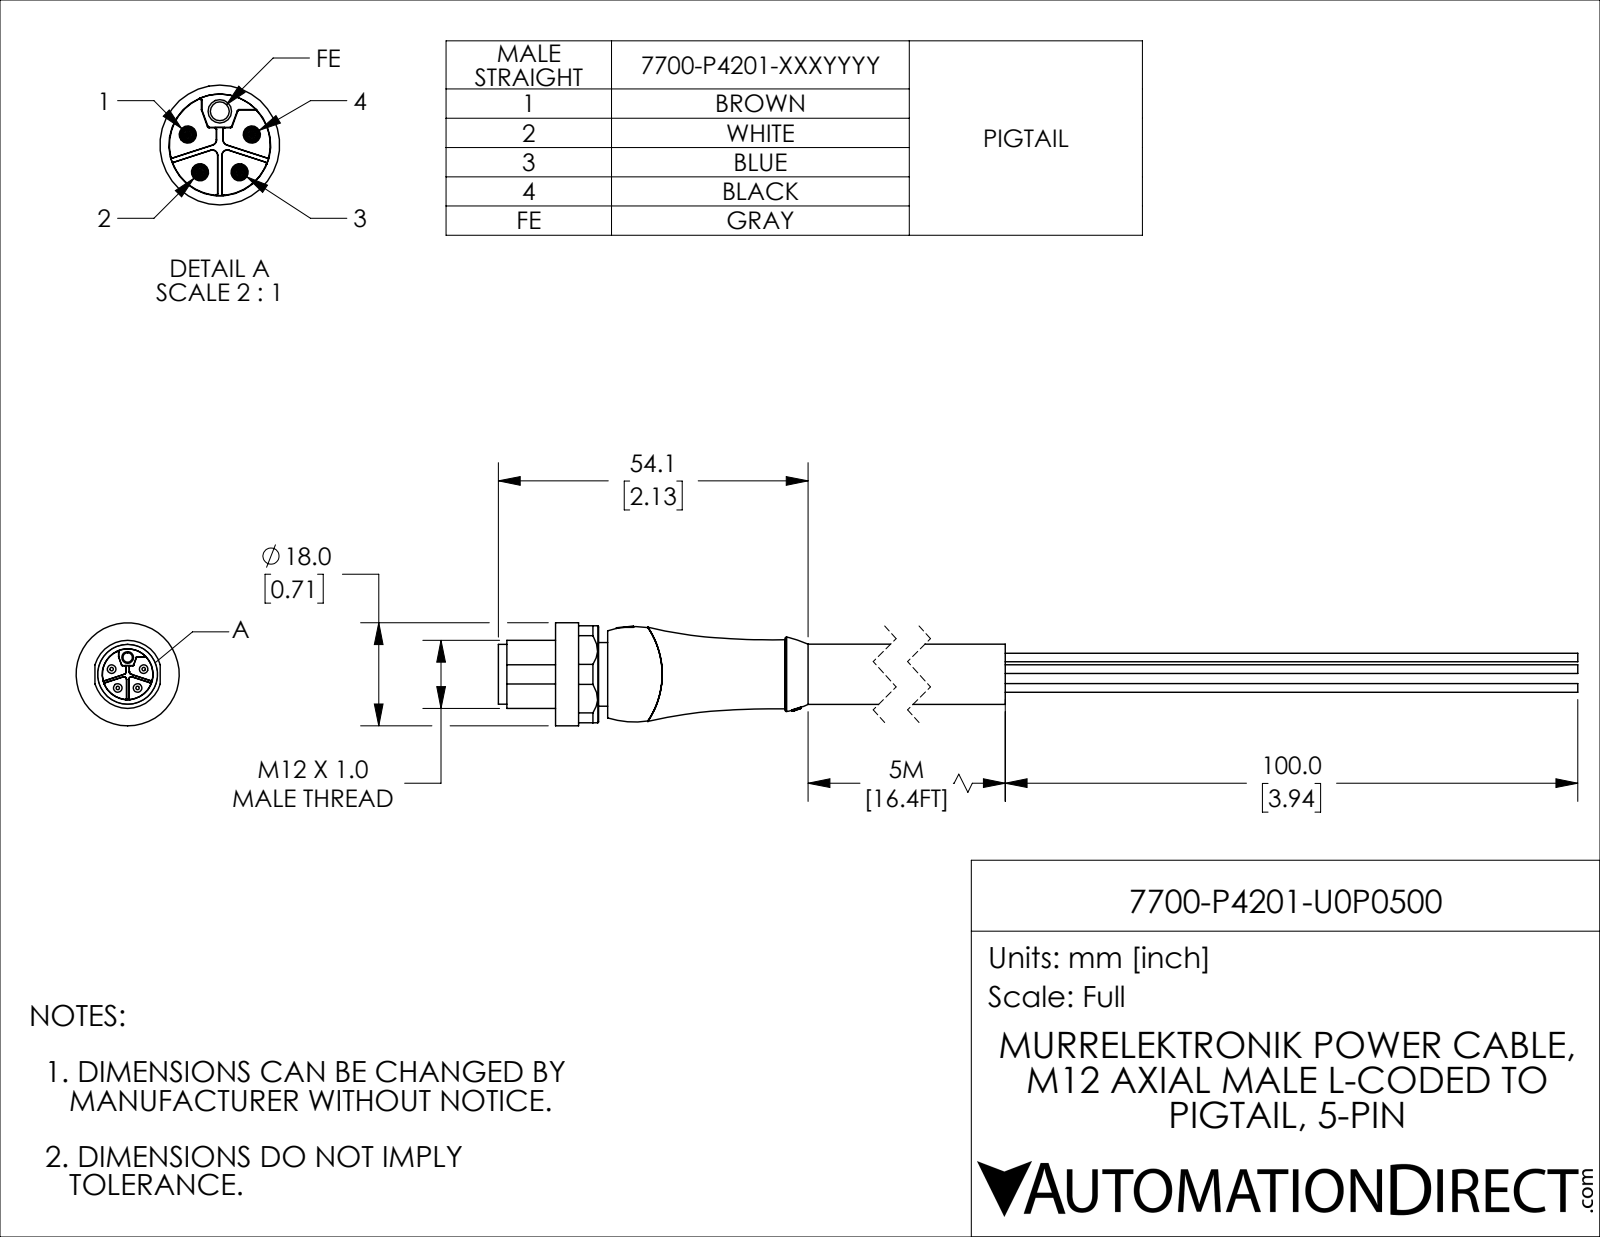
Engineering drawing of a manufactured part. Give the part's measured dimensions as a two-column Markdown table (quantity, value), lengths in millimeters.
| quantity | value |
| --- | --- |
| part name | 7700-P4201-U0P0500 |
| STEP written by | SolidWorks 2021 (CONFIG_CONTROL_DESIGN) |
| units | millimeters |
| bodies | 1 solid, 190 faces (87 planar, 51 cylindrical, 52 other) |
| overall size | 254.1 × 18 × 18 |
| volume | 17 489 mm³ |
| surface area | 9 110 mm² |
| round holes (diameter × count) | 1.65 × 1 |
| round bosses / shafts (diameter × count) | 1.5 × 5, 18 × 1, 11.88 × 1, 11.1 × 1, 10.5 × 1, 10.45 × 1 |
| partial cylindrical surfaces (radius × count) | 0.15 × 6, 1.13 × 1, 8.95 × 1 |
| main face-to-face distances | 9.1, 1.9, 7.2, 144.1, 136.9, 135, 16.94, 1.2, 8.4, 10.3 |
